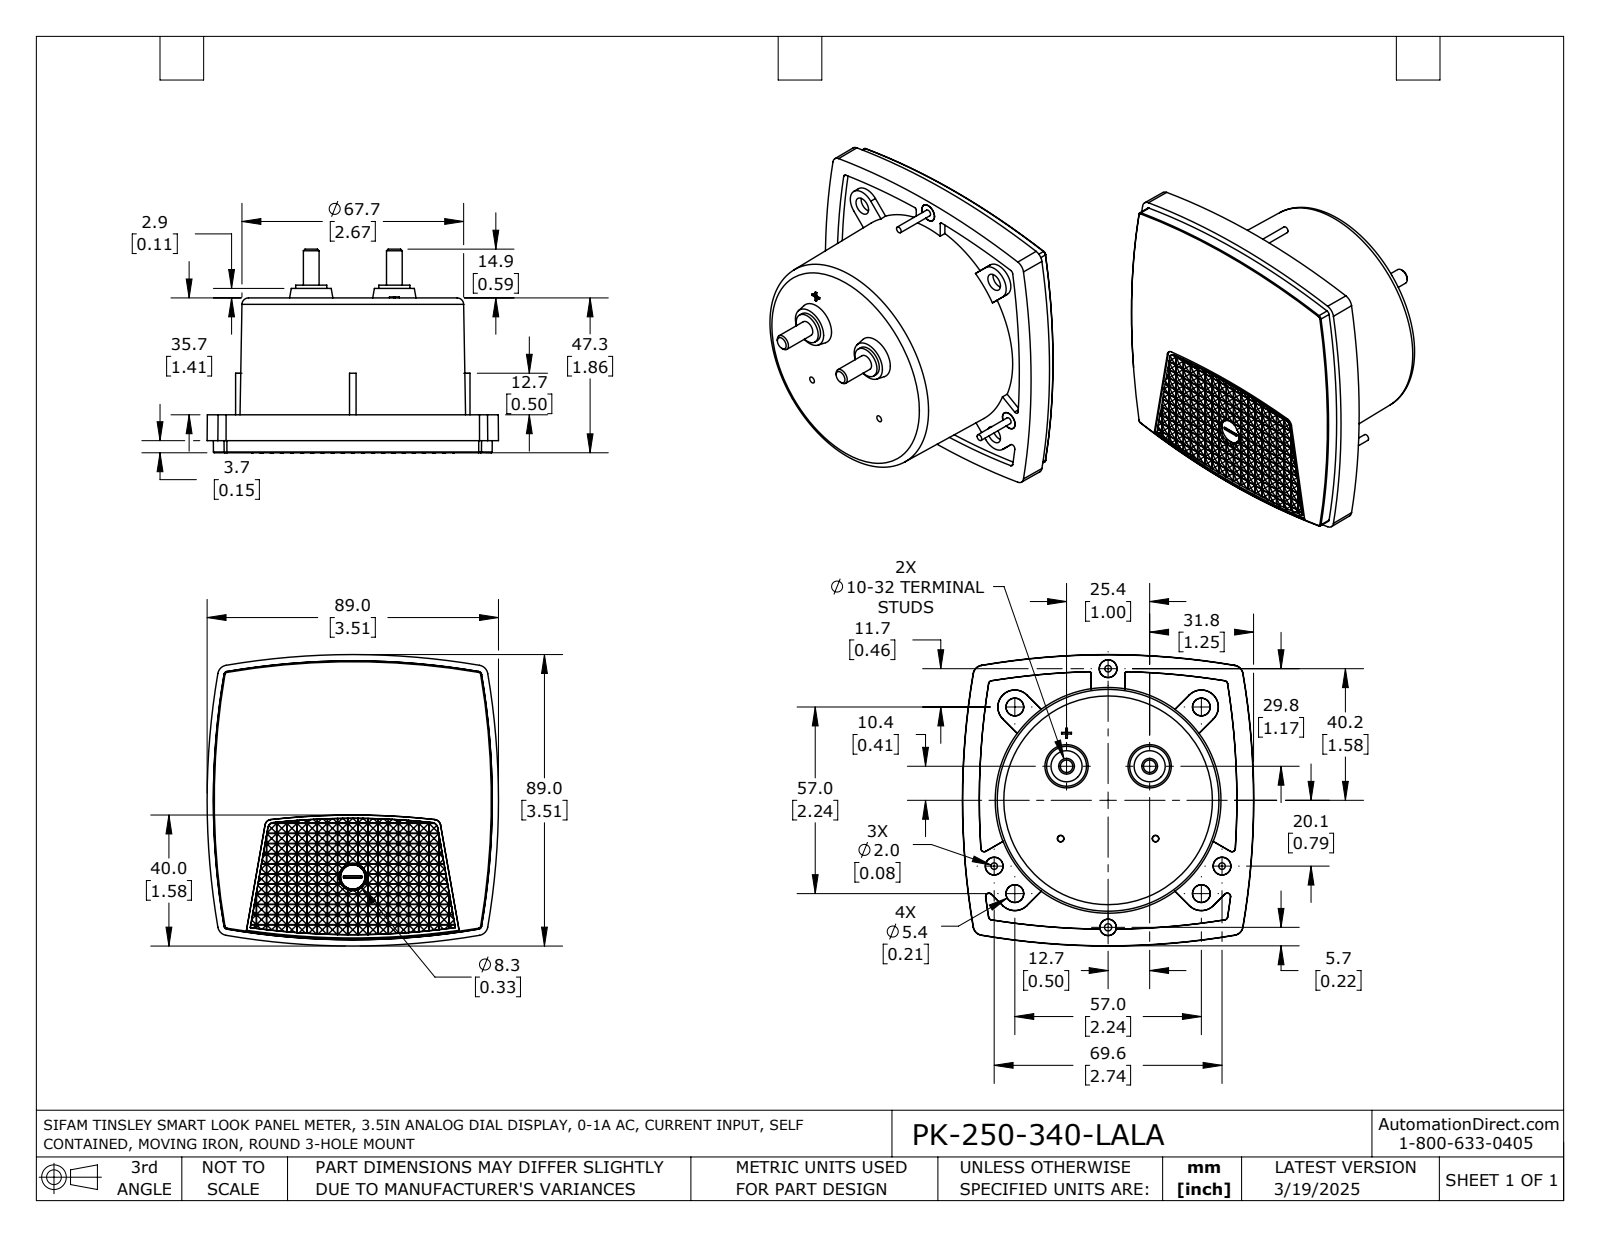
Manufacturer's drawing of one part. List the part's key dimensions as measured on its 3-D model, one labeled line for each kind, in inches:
Part name (STEP PRODUCT): PK-250-340-LALA
STEP written by: SolidWorks 2021 (AUTOMOTIVE_DESIGN)
Units: inches
Bodies: 1 solid, 1078 faces (950 planar, 23 cylindrical, 105 other)
Overall size (bounding box): 3.505 × 3.505 × 2.453
Volume: 12.99 in³ · Surface area: 44.29 in²
Round holes (diameter × count): ⌀0.087 ×1
Round bosses / shafts (diameter × count): ⌀0.213 ×3, ⌀0.079 ×3, ⌀0.374 ×2, ⌀0.189 ×2
Partial cylindrical surfaces — rounded edges, fillets, slot ends (radius × count): R8.961 ×1
Main face-to-face distances: 1.862, 1.406, 0.457, 0.079, 1.484, 0.378, 0.024, 0.096, 0.072, 0.12
